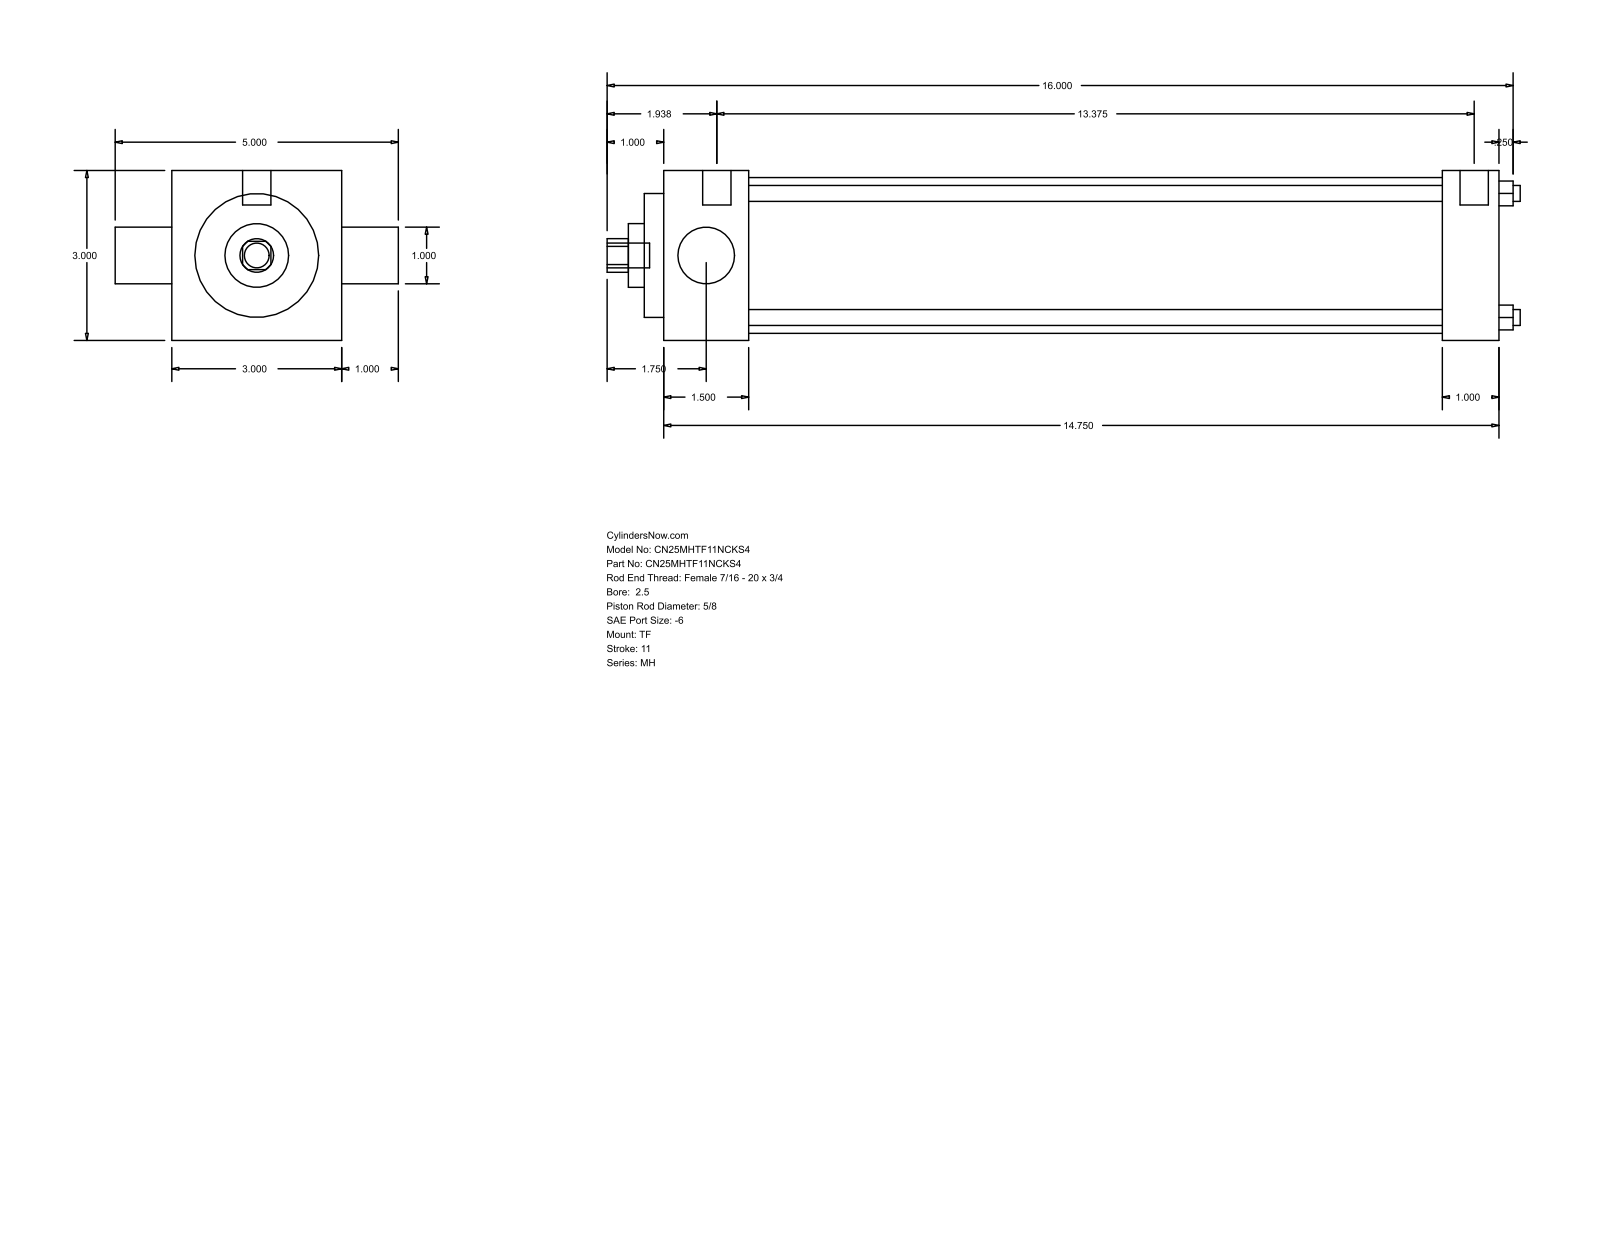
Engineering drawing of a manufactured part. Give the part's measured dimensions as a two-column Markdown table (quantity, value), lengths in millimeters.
| quantity | value |
| --- | --- |
| part name | MH_TF__0250_0.625 |
| STEP written by | GSSL Pune (CONFIG_CONTROL_DESIGN) |
| units | millimeters |
| bodies | 0 solids, 86 faces (61 planar, 25 cylindrical, 0 other) |
| overall size | 409.57 × 127 × 76.2 |
| round holes (diameter × count) | 7.14 × 4, 15.88 × 1, 25.4 × 1, 28.57 × 1, 55.55 × 1, 69.85 × 1 |
| round bosses / shafts (diameter × count) | 5.56 × 3, 12.7 × 2, 11.11 × 1 |
| partial cylindrical surfaces (radius × count) | 7.54 × 1 |
| main face-to-face distances | 76.2, 374.65, 25.4, 38.1, 336.55, 349.25, 311.15, 8.73, 46.83, 357.98 |
| hole center spacings | 39.33, 55.62, 78.66 |
